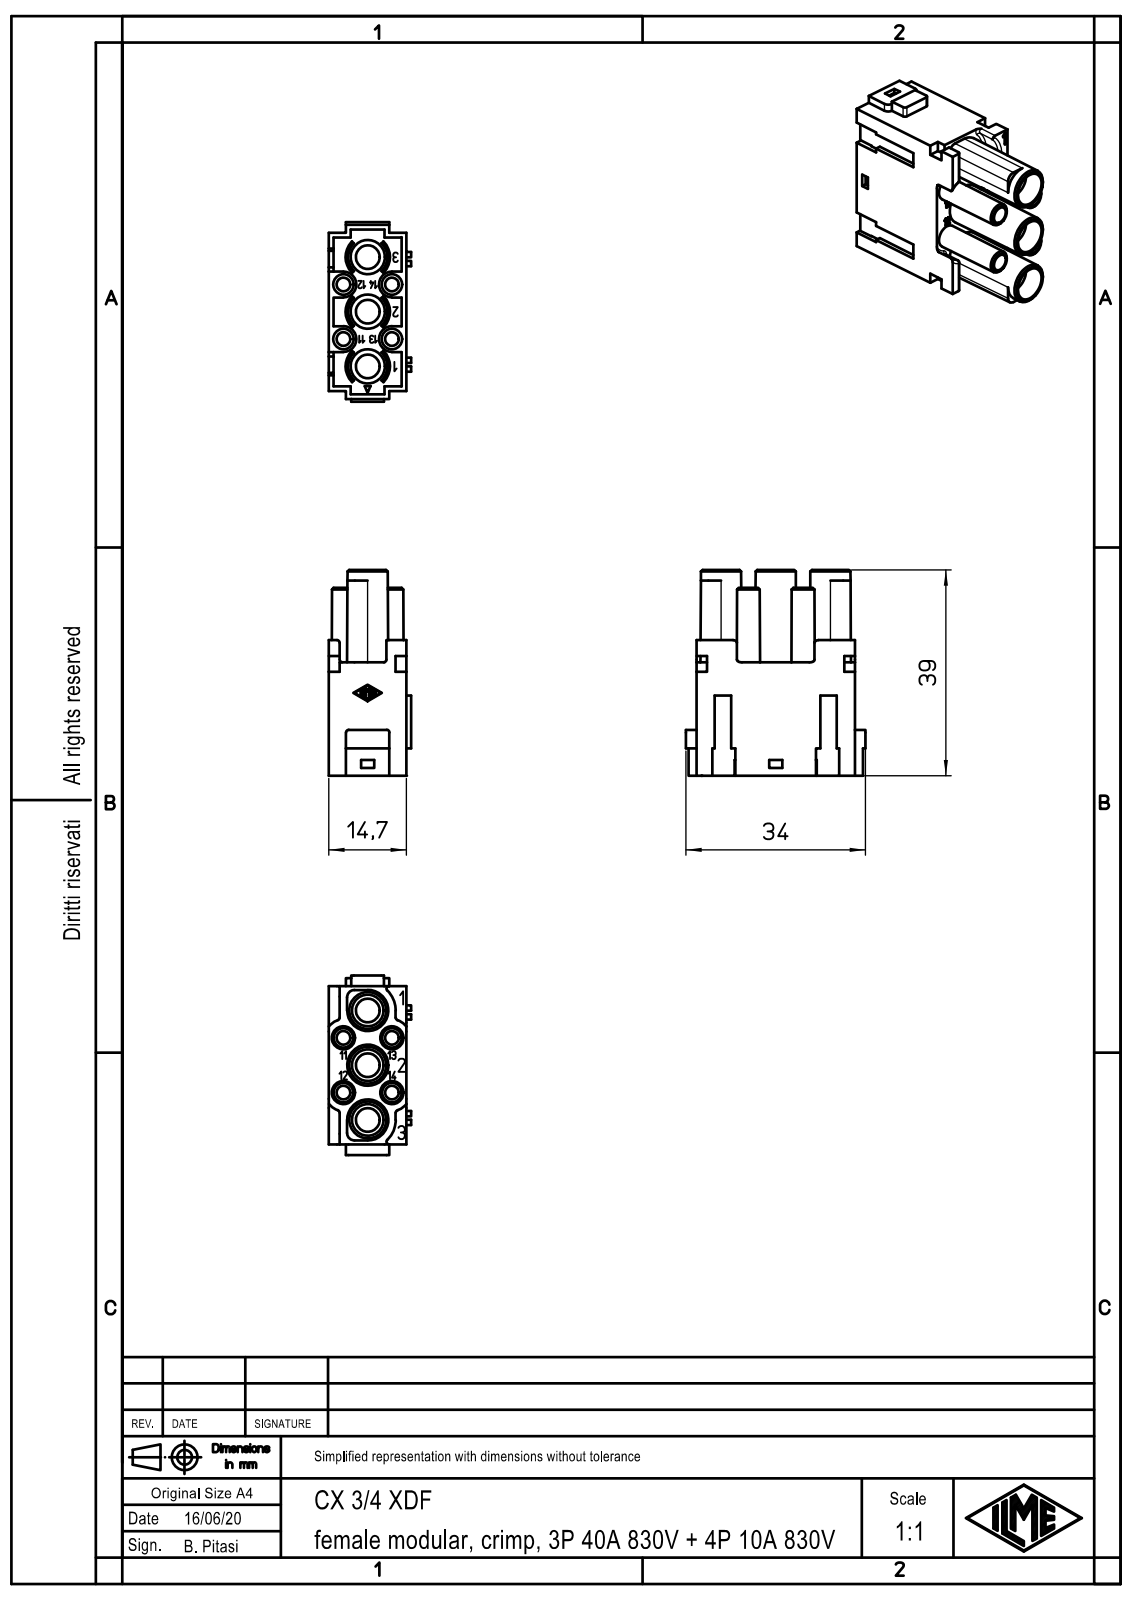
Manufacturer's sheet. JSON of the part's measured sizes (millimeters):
{"part_name": "CX 3-4 XDF", "step_written_by": "Creo Elements/Direct Modeling 20.1B 02-Apr-2019 (C) Parametric Technology GmbH (AUTOMOTIVE_DESIGN)", "units": "millimeters", "bodies": {"solids": 1, "faces": 369, "planar": 221, "cylindrical": 74, "other": 74}, "overall_size": [39, 34, 15.6], "volume_mm3": 7941, "surface_area_mm2": 9836, "round_holes": [[2.6, 4], [3.15, 4], [3.9, 4], [4.5, 3], [6.5, 3]], "partial_cylinders_radius": [[0.5, 14], [2.45, 4], [2.6, 4], [3.5, 4], [1, 2], [1.4, 2], [1.5, 2], [5.3, 2]], "face_to_face_distances": [14.7, 1, 30, 0.9, 1.15, 13.7, 21.5, 2.05, 12.8, 1.05], "hole_center_spacings": [6.92, 6.93, 10.35, 9.2, 13.85, 16.19, 16.2, 20.7]}
